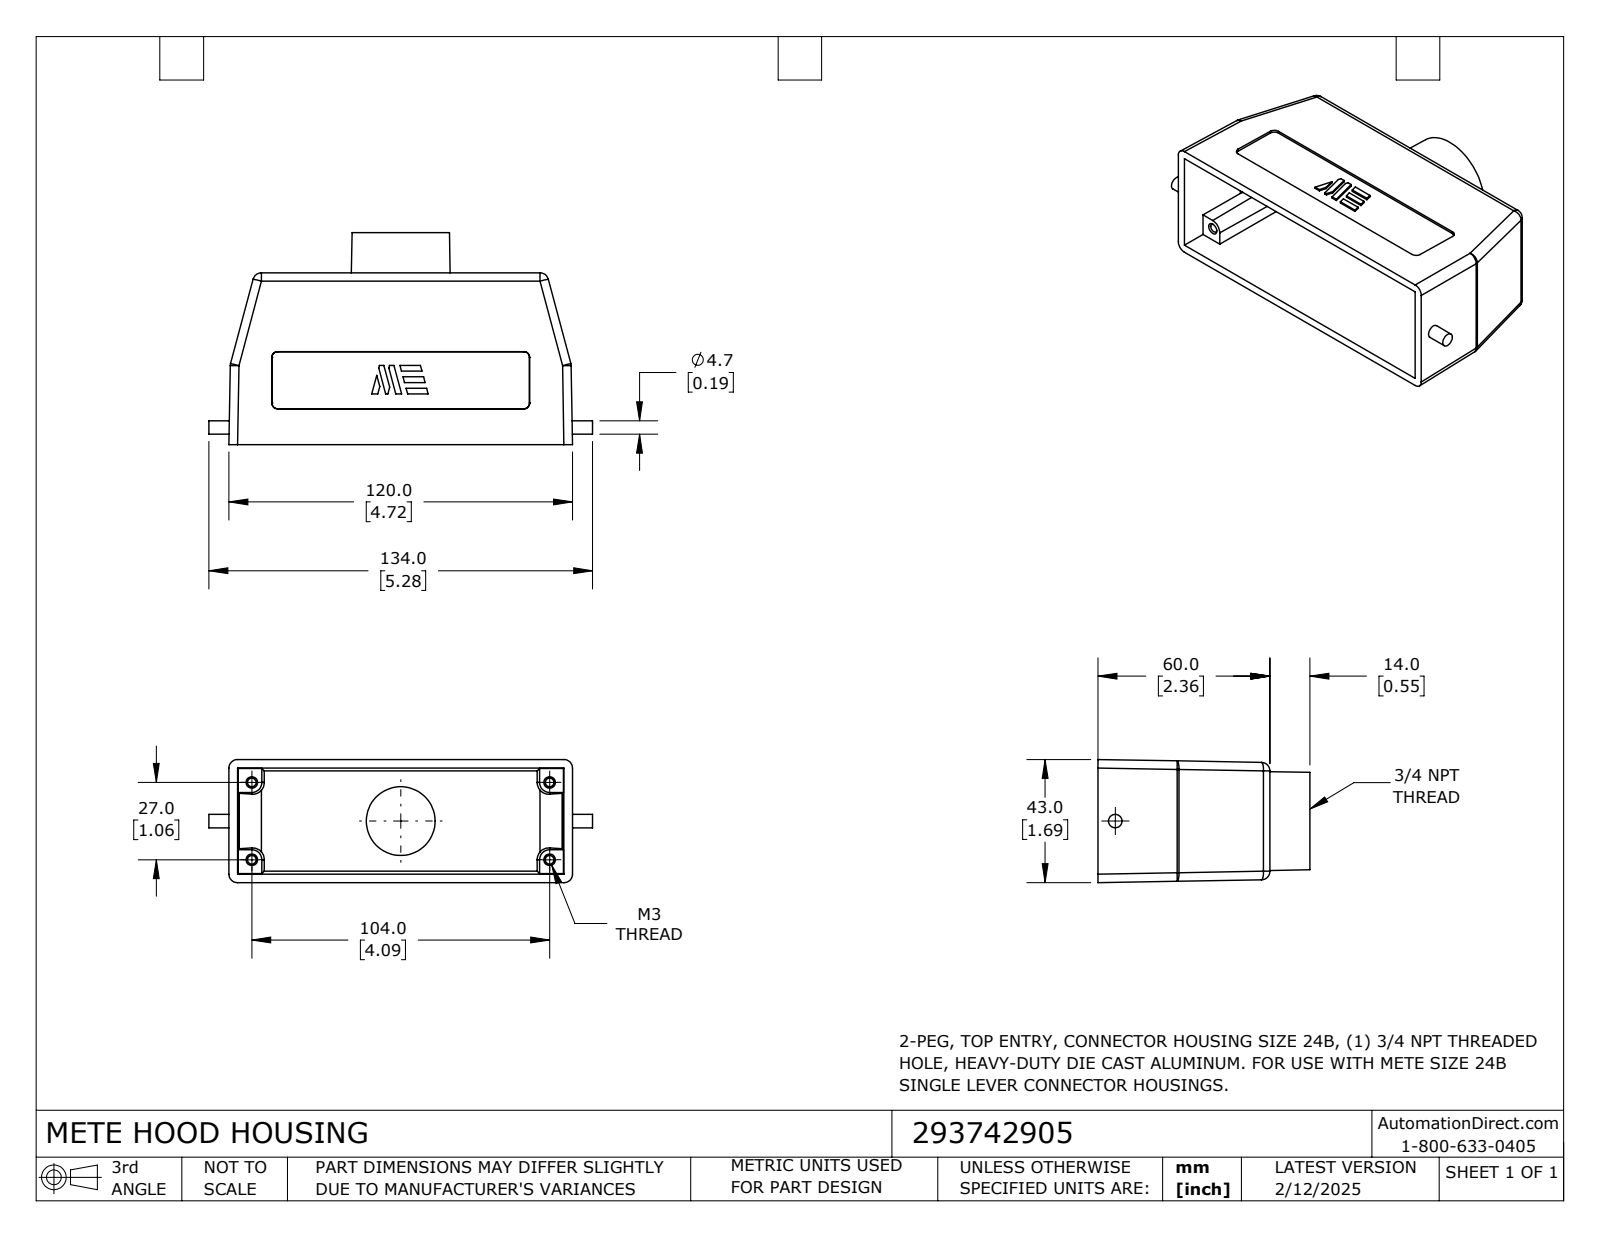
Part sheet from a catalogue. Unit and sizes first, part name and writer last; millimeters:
Units: millimetres
Overall size (bounding box): 134 × 74 × 43
Round holes (diameter × count): ⌀3 ×4, ⌀24 ×1, ⌀27 ×1
Round bosses / shafts (diameter × count): ⌀4.7 ×1
Partial cylindrical surfaces — rounded edges, fillets, slot ends (radius × count): R3 ×14, R2 ×8, R2.9 ×2
Main face-to-face distances: 3, 2.2, 0.8, 8.4, 11.4, 57, 60, 10.6, 74, 17
Hole centre spacings: 53.7, 27, 104, 107.4
Volume: 73 430 mm³ · Surface area: 46 530 mm²
Bodies: 1 solid, 173 faces (111 planar, 40 cylindrical, 22 other)
Part name (STEP PRODUCT): 293742905
STEP written by: SolidWorks 2024 (CONFIG_CONTROL_DESIGN)
